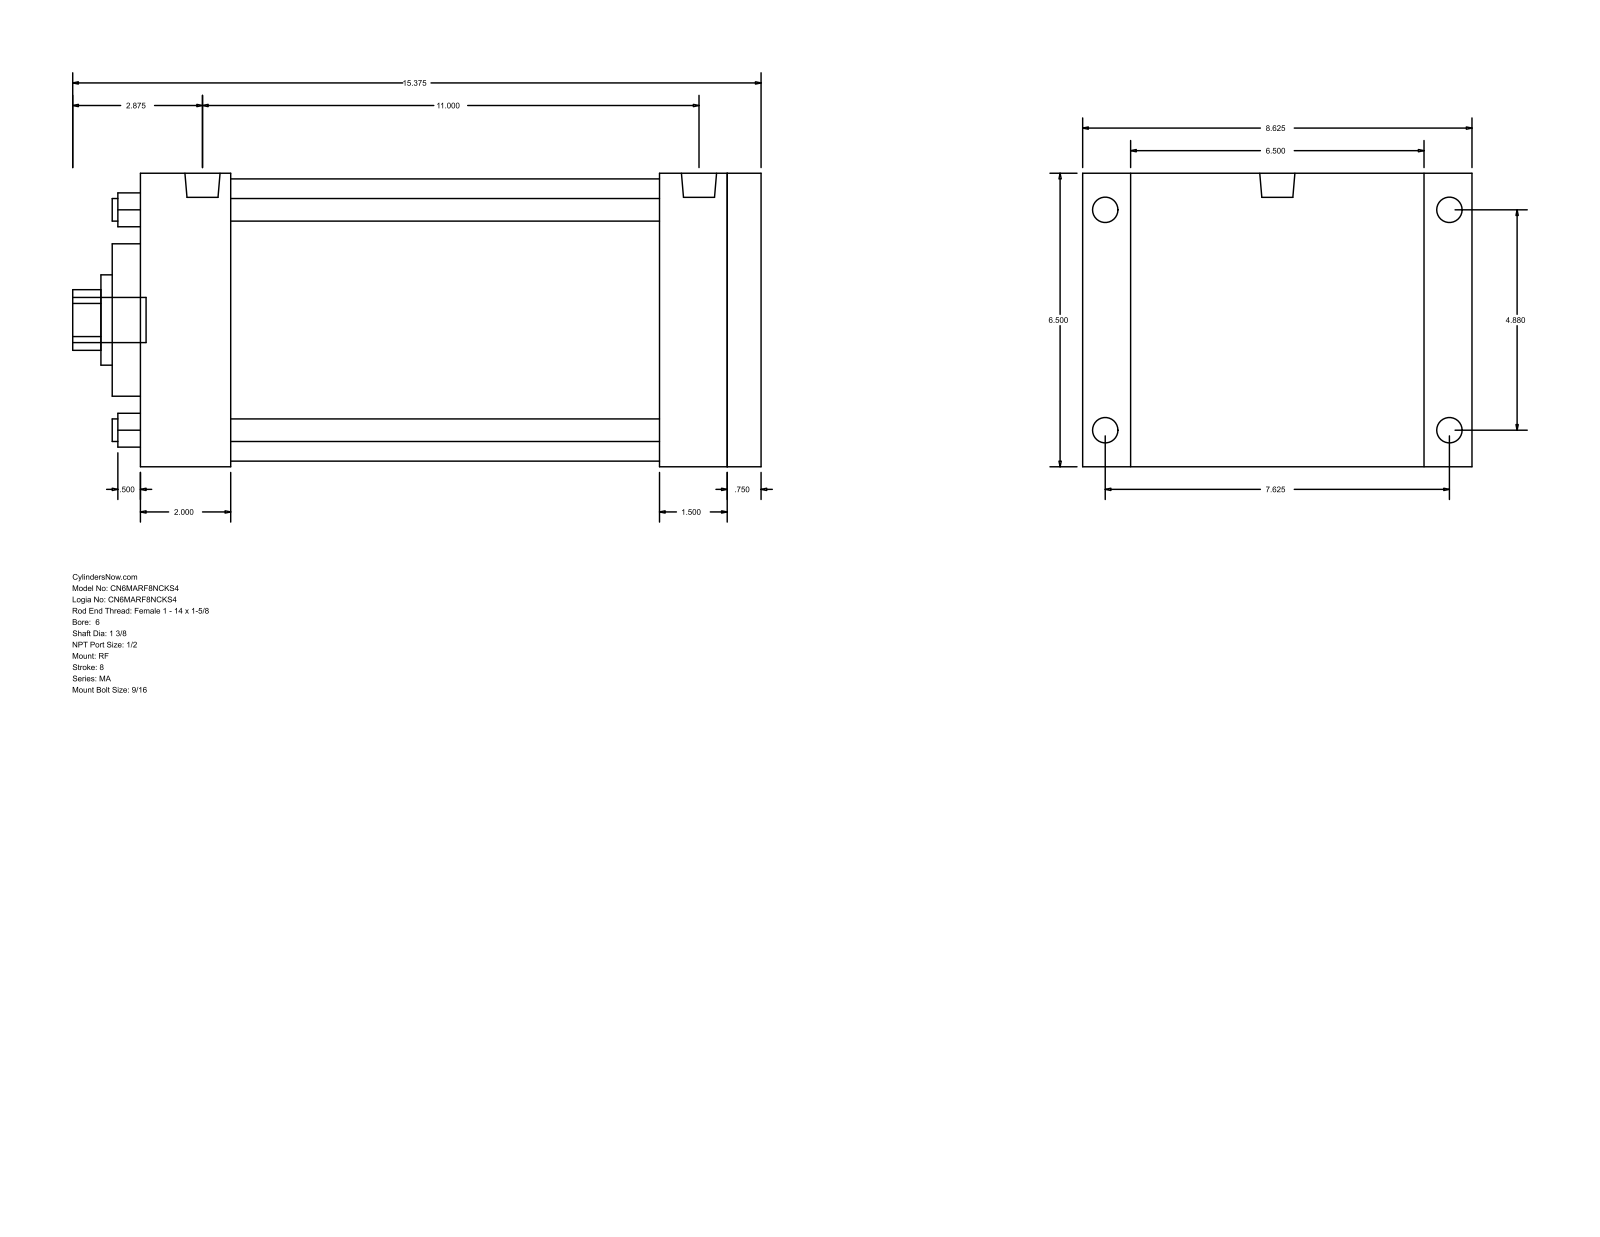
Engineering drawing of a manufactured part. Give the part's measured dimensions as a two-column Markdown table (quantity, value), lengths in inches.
| quantity | value |
| --- | --- |
| part name | MA_RF__0600_1.375 |
| STEP written by | GSSL Pune (CONFIG_CONTROL_DESIGN) |
| units | inches |
| bodies | 0 solids, 94 faces (65 planar, 29 cylindrical, 0 other) |
| overall size | 15.375 × 8.625 × 6.5 |
| round holes (diameter × count) | 0.5 × 4, 1.375 × 1, 2 × 1, 3.375 × 1, 6.25 × 1 |
| round bosses / shafts (diameter × count) | 0.687 × 4, 0.563 × 4, 0.778 × 2, 1 × 1 |
| partial cylindrical surfaces (radius × count) | 0.672 × 1 |
| main face-to-face distances | 6.5, 13.875, 0.75, 13.125, 1.5, 2, 11.125, 11.875, 11.625, 9.625 |
| hole center spacings | 3.451, 4.88, 6.902 |
